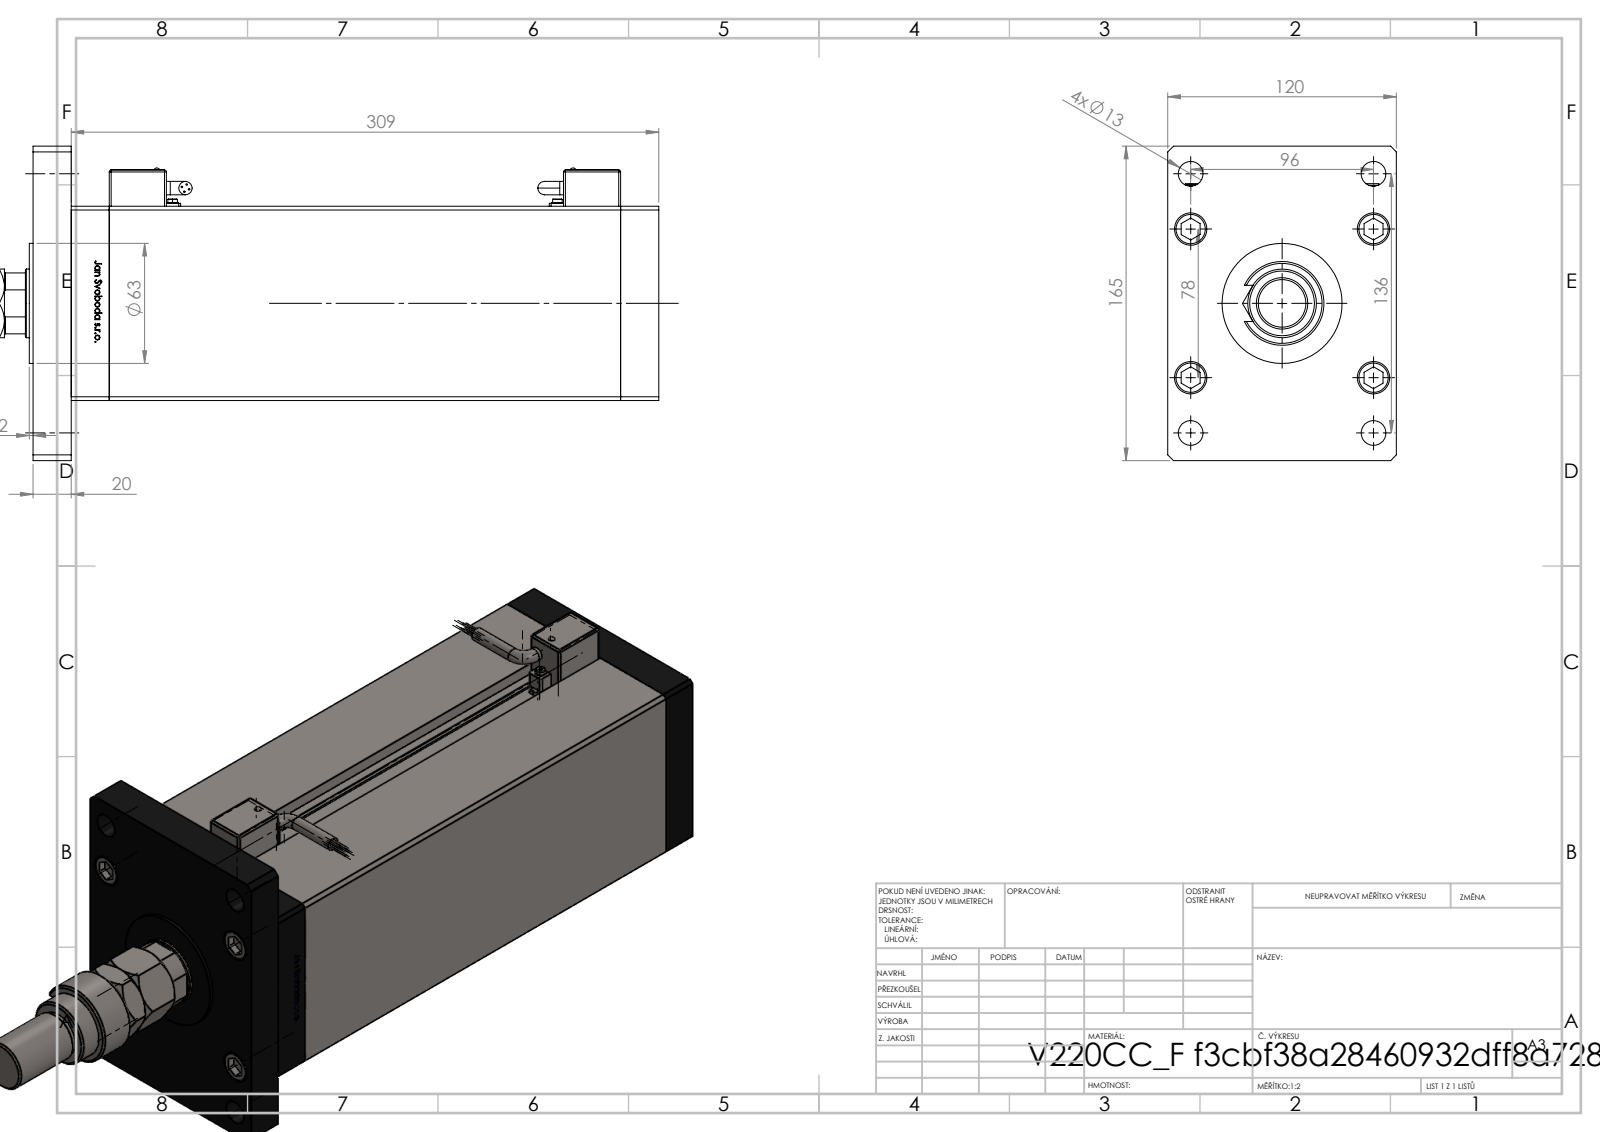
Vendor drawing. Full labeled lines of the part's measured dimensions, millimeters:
Part name (STEP PRODUCT): Magnetic_Switch_MSU4; MFA; V220C_F_MIDDLE; V220C BACK_F (+5 more)
STEP written by: SolidWorks 2019 (CONFIG_CONTROL_DESIGN)
Units: millimetres
Bodies: 23 solids, 1600 faces (623 planar, 291 cylindrical, 686 other)
Overall size (bounding box): 454 × 165 × 120
Volume: 3 746 000 mm³ · Surface area: 446 838 mm²
Round holes (diameter × count): ⌀13.5 ×5, ⌀18 ×5, ⌀12 ×4, ⌀13 ×4, ⌀17 ×4, ⌀2 ×2, ⌀3.6 ×2, ⌀5 ×2, ⌀7 ×2, ⌀13.16 ×2, ⌀25.5 ×1, ⌀36 ×1
Round bosses / shafts (diameter × count): ⌀8 ×9, ⌀0.85 ×8, ⌀17 ×5, ⌀7 ×4, ⌀6 ×2, ⌀3.5 ×2, ⌀2.5 ×2, ⌀63 ×1
Partial cylindrical surfaces — rounded edges, fillets, slot ends (radius × count): R1 ×24, R4 ×4, R0.93 ×2, R9.5 ×1, R15 ×1, R17.5 ×1
Main face-to-face distances: 20, 120, 102, 288.5, 308.5, 268.5, 40, 328.5, 34.25, 2
Hole centre spacings: 41.5, 29, 61.85, 83.23, 96, 100.28, 107, 143.75
